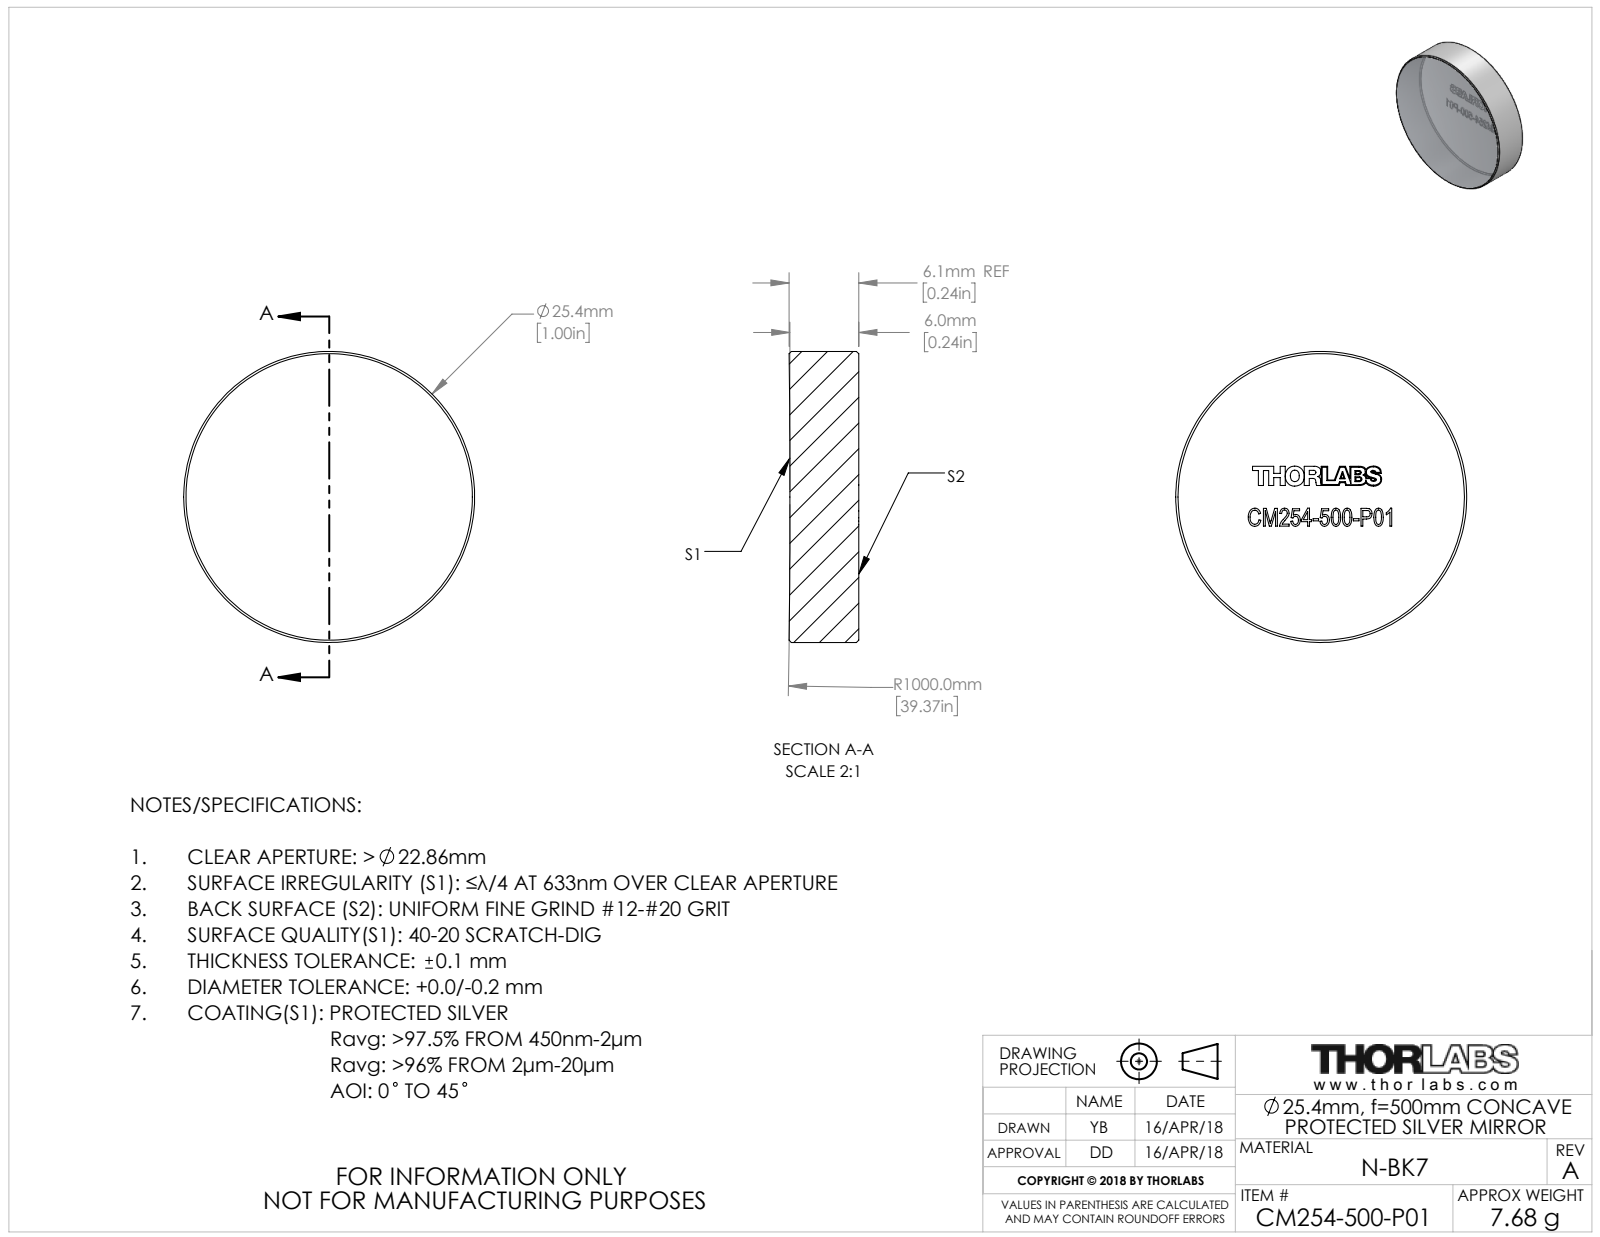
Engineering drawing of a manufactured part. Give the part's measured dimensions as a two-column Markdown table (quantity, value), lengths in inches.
| quantity | value |
| --- | --- |
| part name | TTN153304-E0W |
| STEP written by | SolidWorks 2018 (CONFIG_CONTROL_DESIGN) |
| units | inches |
| bodies | 1 solid, 42 faces (34 planar, 2 cylindrical, 6 other) |
| overall size | 1 × 1 × 0.239 |
| volume | 0.187 in³ |
| surface area | 2.294 in² |
| round bosses / shafts (diameter × count) | 1 × 1 |
